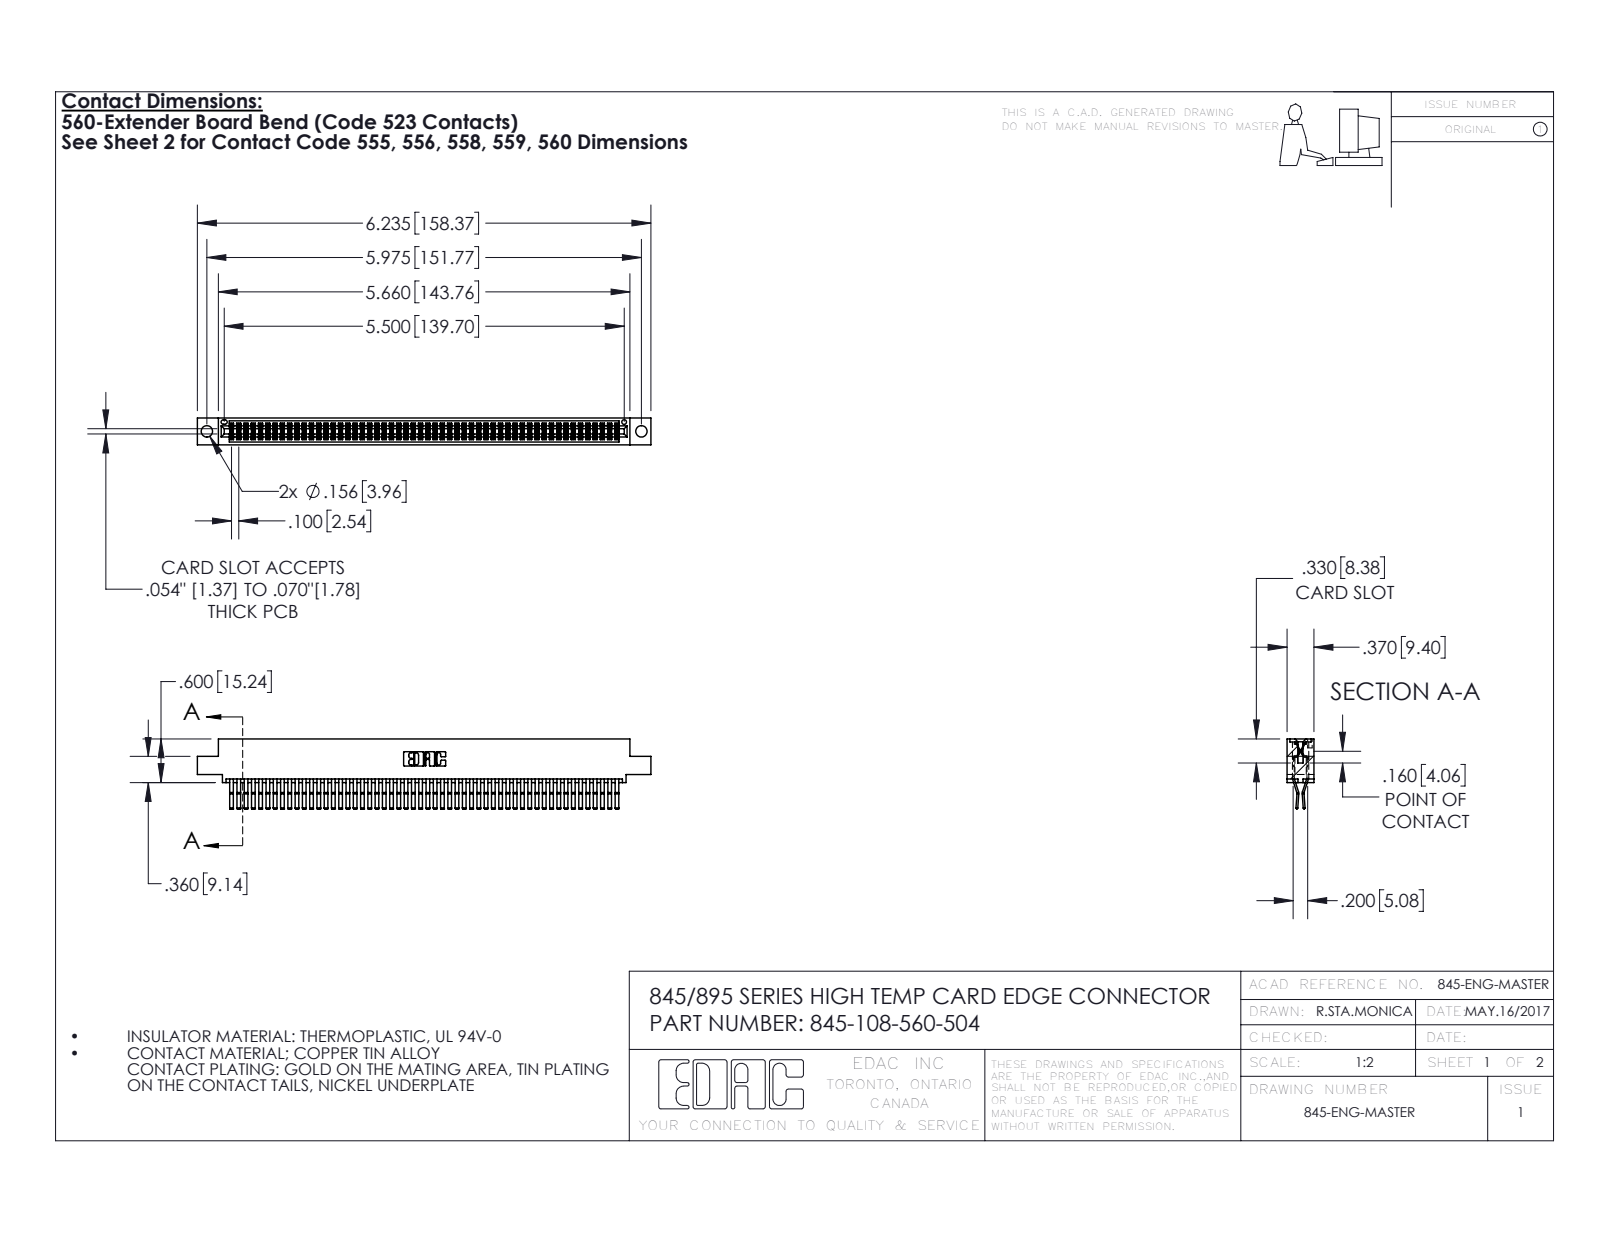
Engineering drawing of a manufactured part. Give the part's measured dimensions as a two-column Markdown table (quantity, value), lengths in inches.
| quantity | value |
| --- | --- |
| part name | 345-292-001_560 Tail; 345 Part_0.110 Offset - 0.156 Dia-TH; 345-108-560-504 |
| STEP written by | SolidWorks 2016 (CONFIG_CONTROL_DESIGN) |
| units | inches |
| bodies | 109 solids, 5746 faces (3648 planar, 2098 cylindrical, 0 other) |
| overall size | 6.235 × 0.962 × 0.37 |
| volume | 0.979 in³ |
| surface area | 39.79 in² |
| round holes (diameter × count) | 0.156 × 2, 0.064 × 1 |
| partial cylindrical surfaces (radius × count) | 0.006 × 162, 0.01 × 22, 0.007 × 6, 0.031 × 6, 0.026 × 3, 0.01 × 2, 0.014 × 2, 0.019 × 2 |
| main face-to-face distances | 0.025, 0.298, 0.072, 0.37, 0.2, 0.098, 0.272, 0.225, 0.175, 0.149 |
| hole center spacings | 0.27, 5.739, 5.975 |
